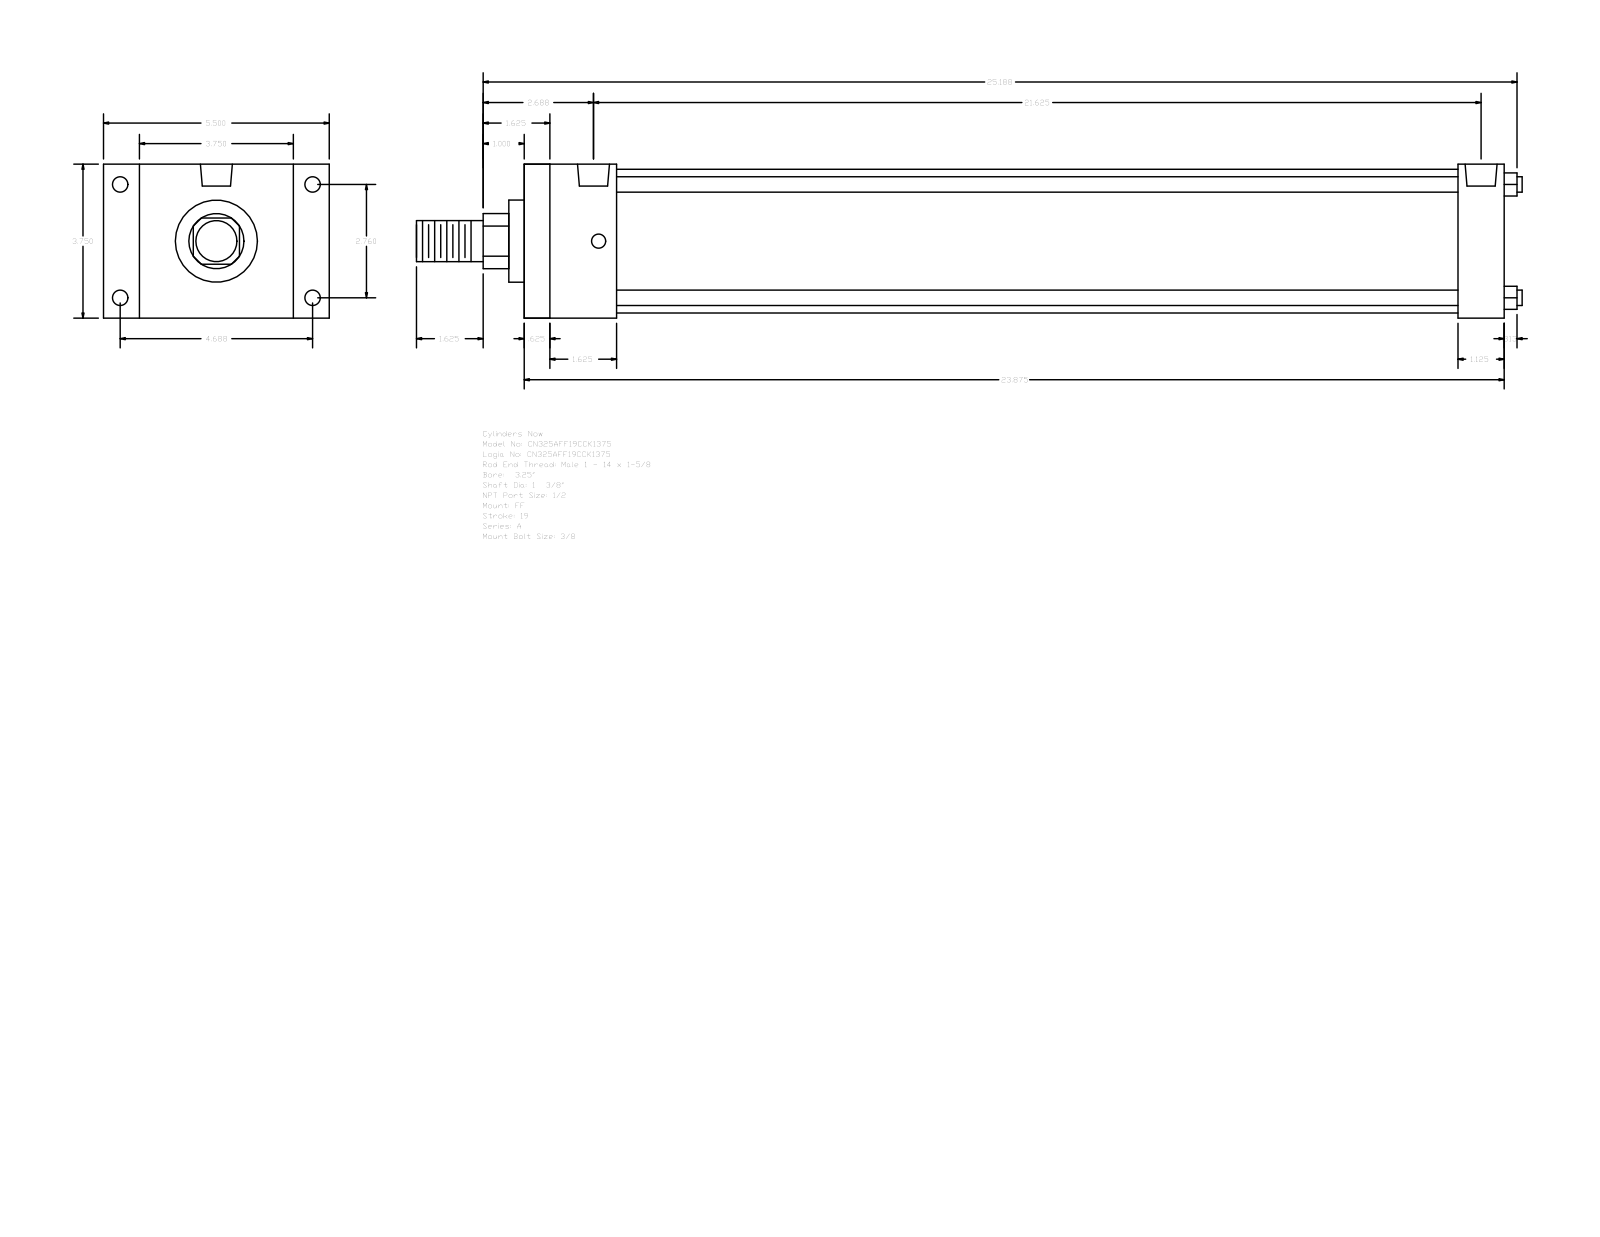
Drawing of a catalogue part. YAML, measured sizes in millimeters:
part_name: "A_FF__0325_1.375"
step_written_by: "GSSL Pune (CONFIG_CONTROL_DESIGN)"
units: millimeters
bodies: {solids: 0, faces: 92, planar: 64, cylindrical: 28, other: 0}
overall_size: [684.21, 139.7, 95.25]
round_holes:
  - {diameter: 8.73, count: 4}
  - {diameter: 9.53, count: 4}
  - {diameter: 19.77, count: 2}
round_bosses_or_shafts:
  - {diameter: 9.53, count: 4}
  - {diameter: 88.9, count: 1}
  - {diameter: 50.8, count: 1}
  - {diameter: 34.92, count: 1}
  - {diameter: 25.4, count: 1}
partial_cylinders:
  - {radius: 17.06, count: 1}
face_to_face_distances: [95.24, 606.43, 15.87, 590.56, 57.15, 28.58, 22.23, 117.47, 577.85, 41.28]
hole_center_spacings: [3.18, 70.1, 119.06, 138.16, 542.92, 546.1, 549.28]
